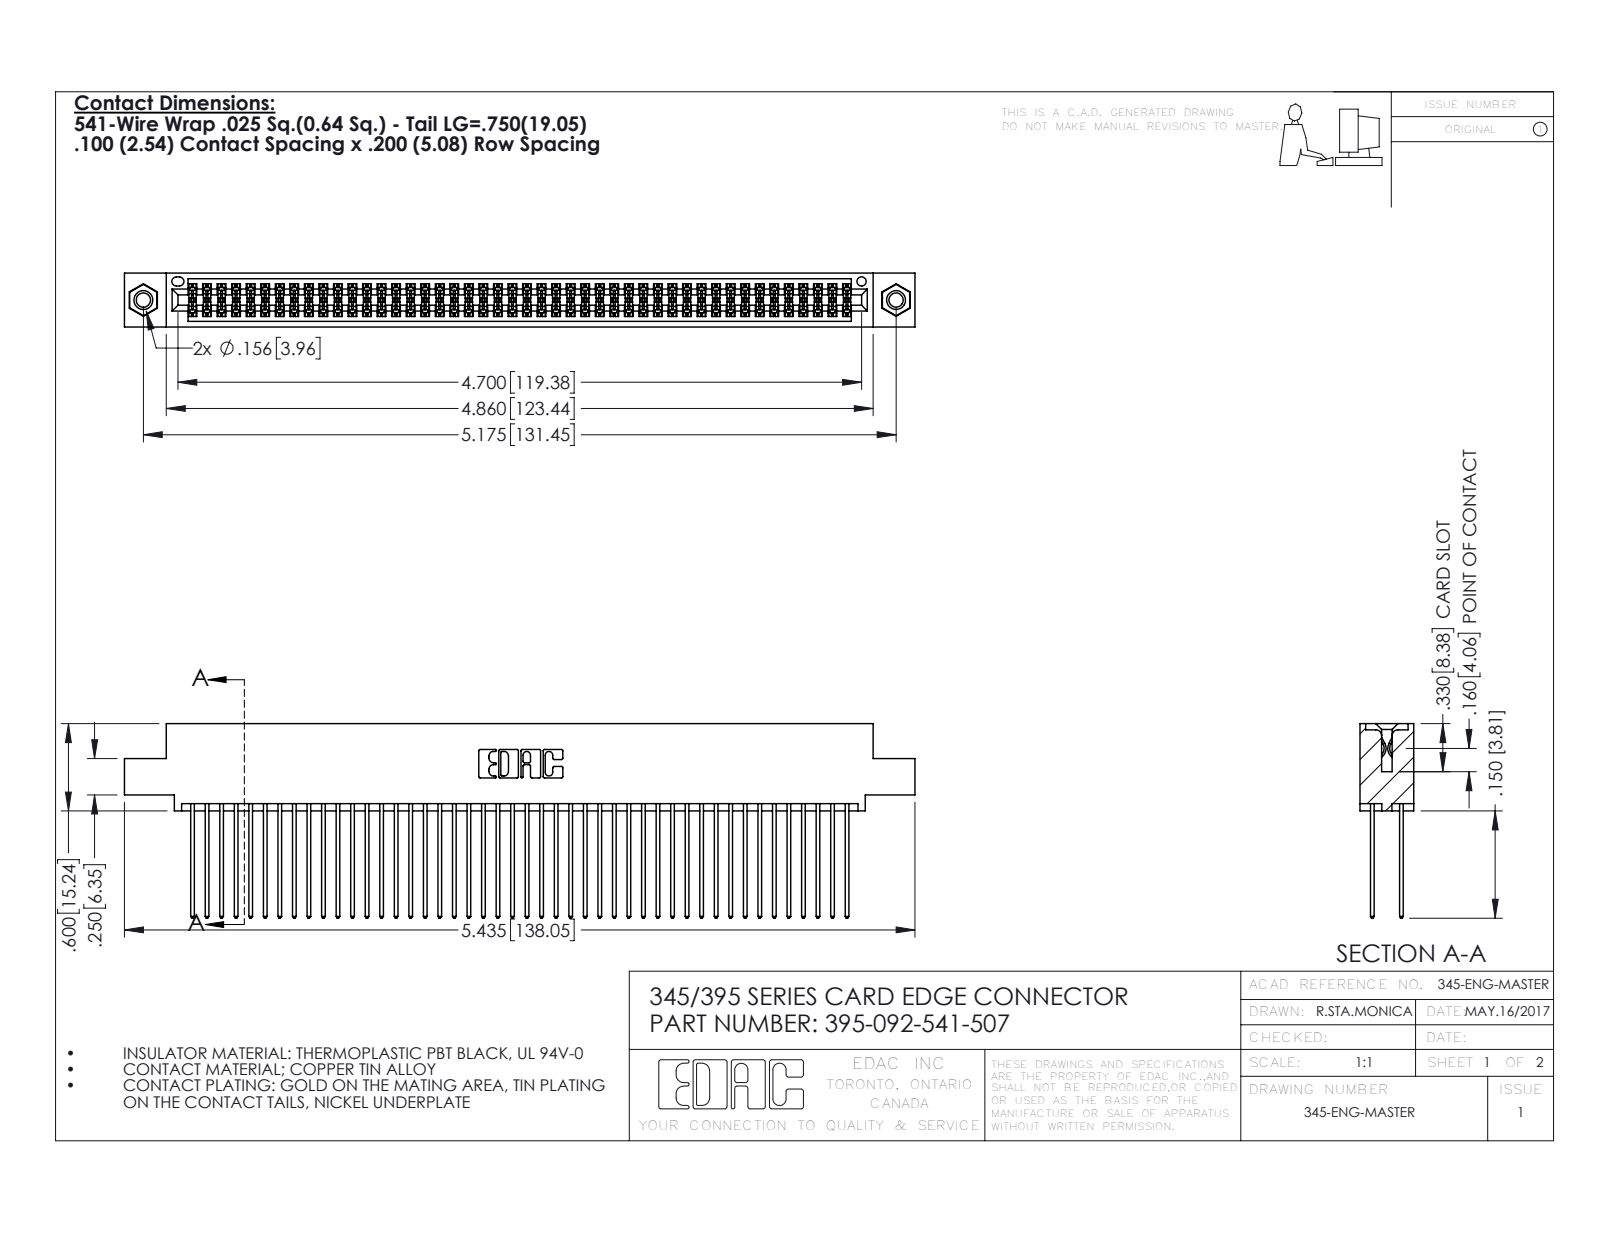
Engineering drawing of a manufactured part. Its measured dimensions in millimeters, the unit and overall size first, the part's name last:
Units: millimetres
Overall size (bounding box): 138 × 34 × 9.4
Round holes (diameter × count): ⌀2.5 ×2, ⌀3.2 ×2, ⌀4 ×2, ⌀1.6 ×1
Round bosses / shafts (diameter × count): ⌀3.9 ×2
Partial cylindrical surfaces — rounded edges, fillets, slot ends (radius × count): R0.2 ×138, R0.3 ×92, R0.3 ×22, R0.2 ×6, R0.8 ×6, R0.7 ×3, R0.4 ×2, R0.5 ×2
Main face-to-face distances: 1.8, 7.6, 5.1, 2.5, 6.9, 0.6, 5.7, 9.4, 4.4, 3.8
Hole centre spacings: 6.9, 125.5, 131.4
Volume: 13 900 mm³ · Surface area: 23 210 mm²
Bodies: 95 solids, 4790 faces (3152 planar, 1622 cylindrical, 16 other)
Part name (STEP PRODUCT): 345-250-001_345-250-005-103; 395-092-541-507; 345 Part_0.110 Offset - 0.156 Dia-TI; 345-292-001_345-293-141
STEP written by: SolidWorks 2016 (CONFIG_CONTROL_DESIGN)
